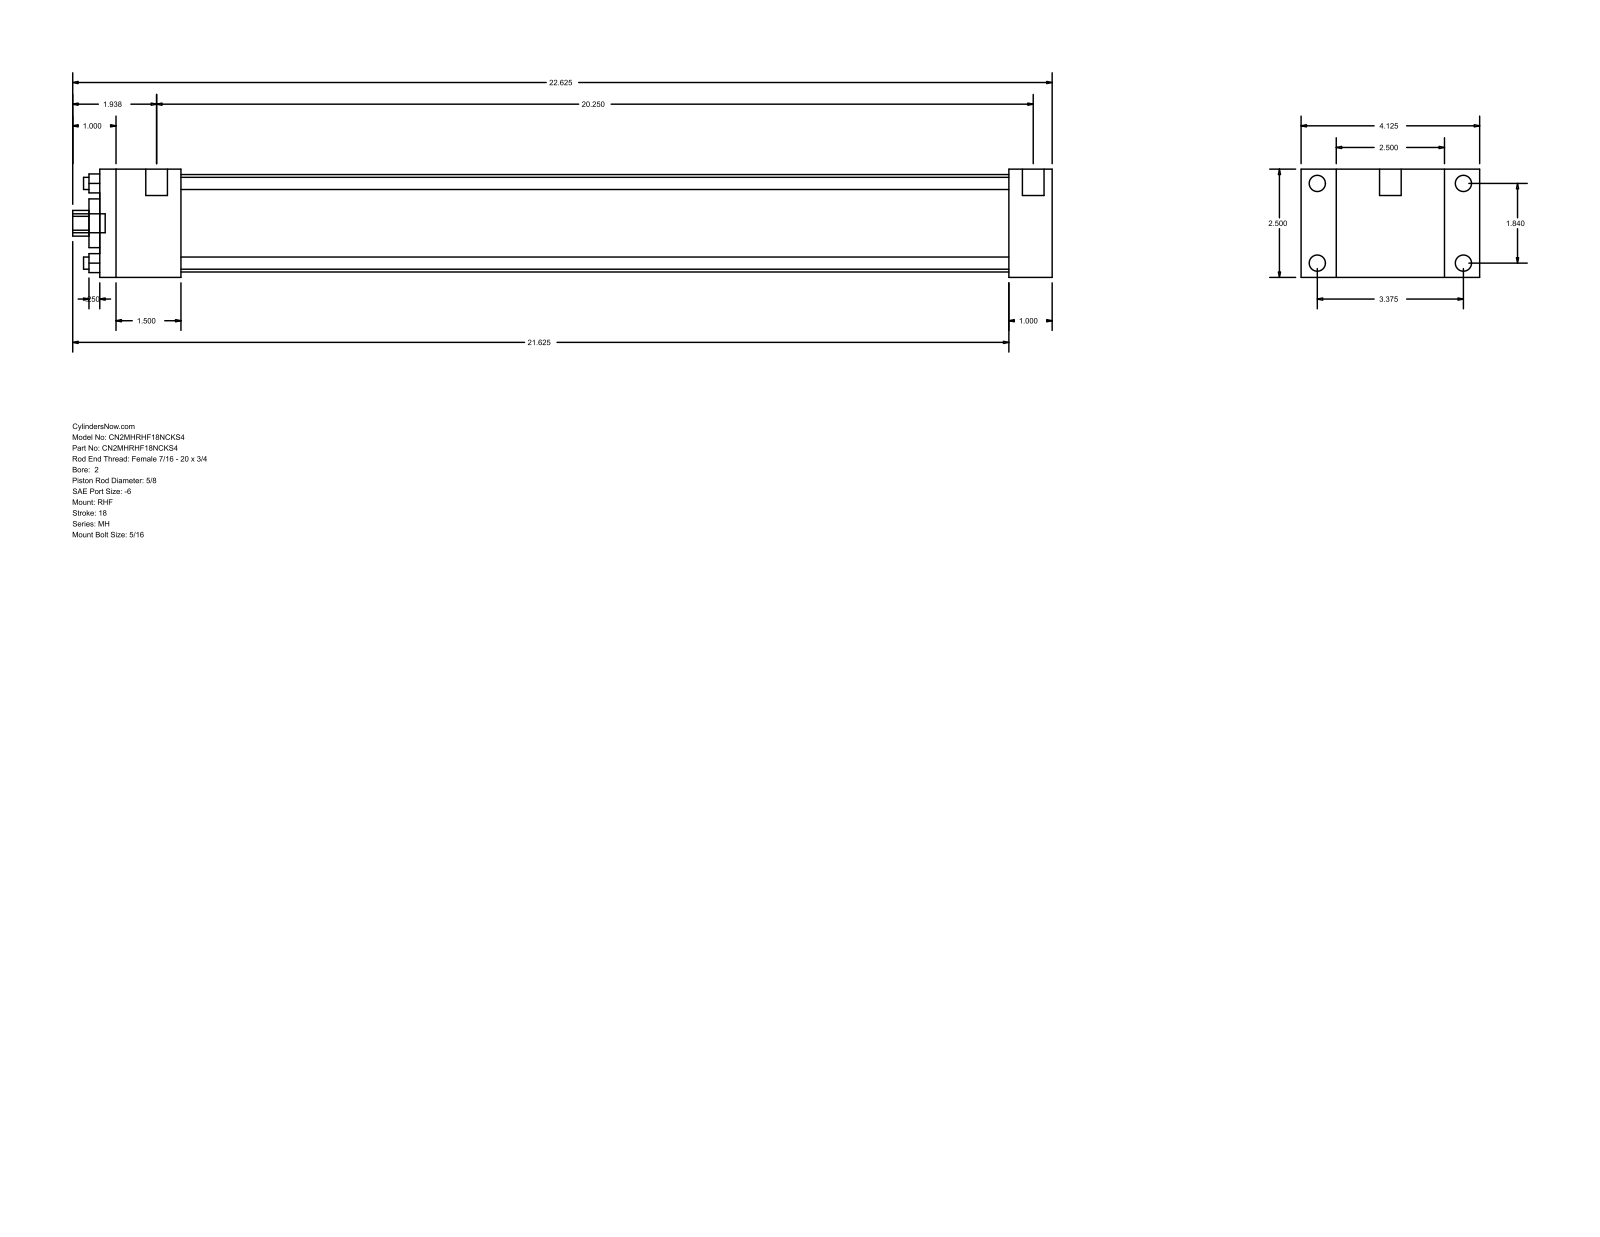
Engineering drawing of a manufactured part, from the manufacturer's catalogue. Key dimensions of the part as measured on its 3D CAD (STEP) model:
Part name (STEP PRODUCT): MH_RHF__0200_0.625
STEP written by: GSSL Pune (CONFIG_CONTROL_DESIGN)
Units: millimetres
Bodies: 0 solids, 88 faces (60 planar, 28 cylindrical, 0 other)
Overall size (bounding box): 574.67 × 104.78 × 63.5
Round holes (diameter × count): ⌀7.14 ×4, ⌀15.88 ×1, ⌀28.57 ×1, ⌀57.15 ×1
Round bosses / shafts (diameter × count): ⌀9.53 ×4, ⌀5.56 ×4, ⌀12.7 ×2, ⌀11.11 ×1
Partial cylindrical surfaces — rounded edges, fillets, slot ends (radius × count): R7.54 ×1
Main face-to-face distances: 63.5, 25.4, 20.64, 84.14, 533.39, 558.79, 104.78, 47.62, 485.77, 511.17
Hole centre spacings: 33.05, 46.74, 66.1
